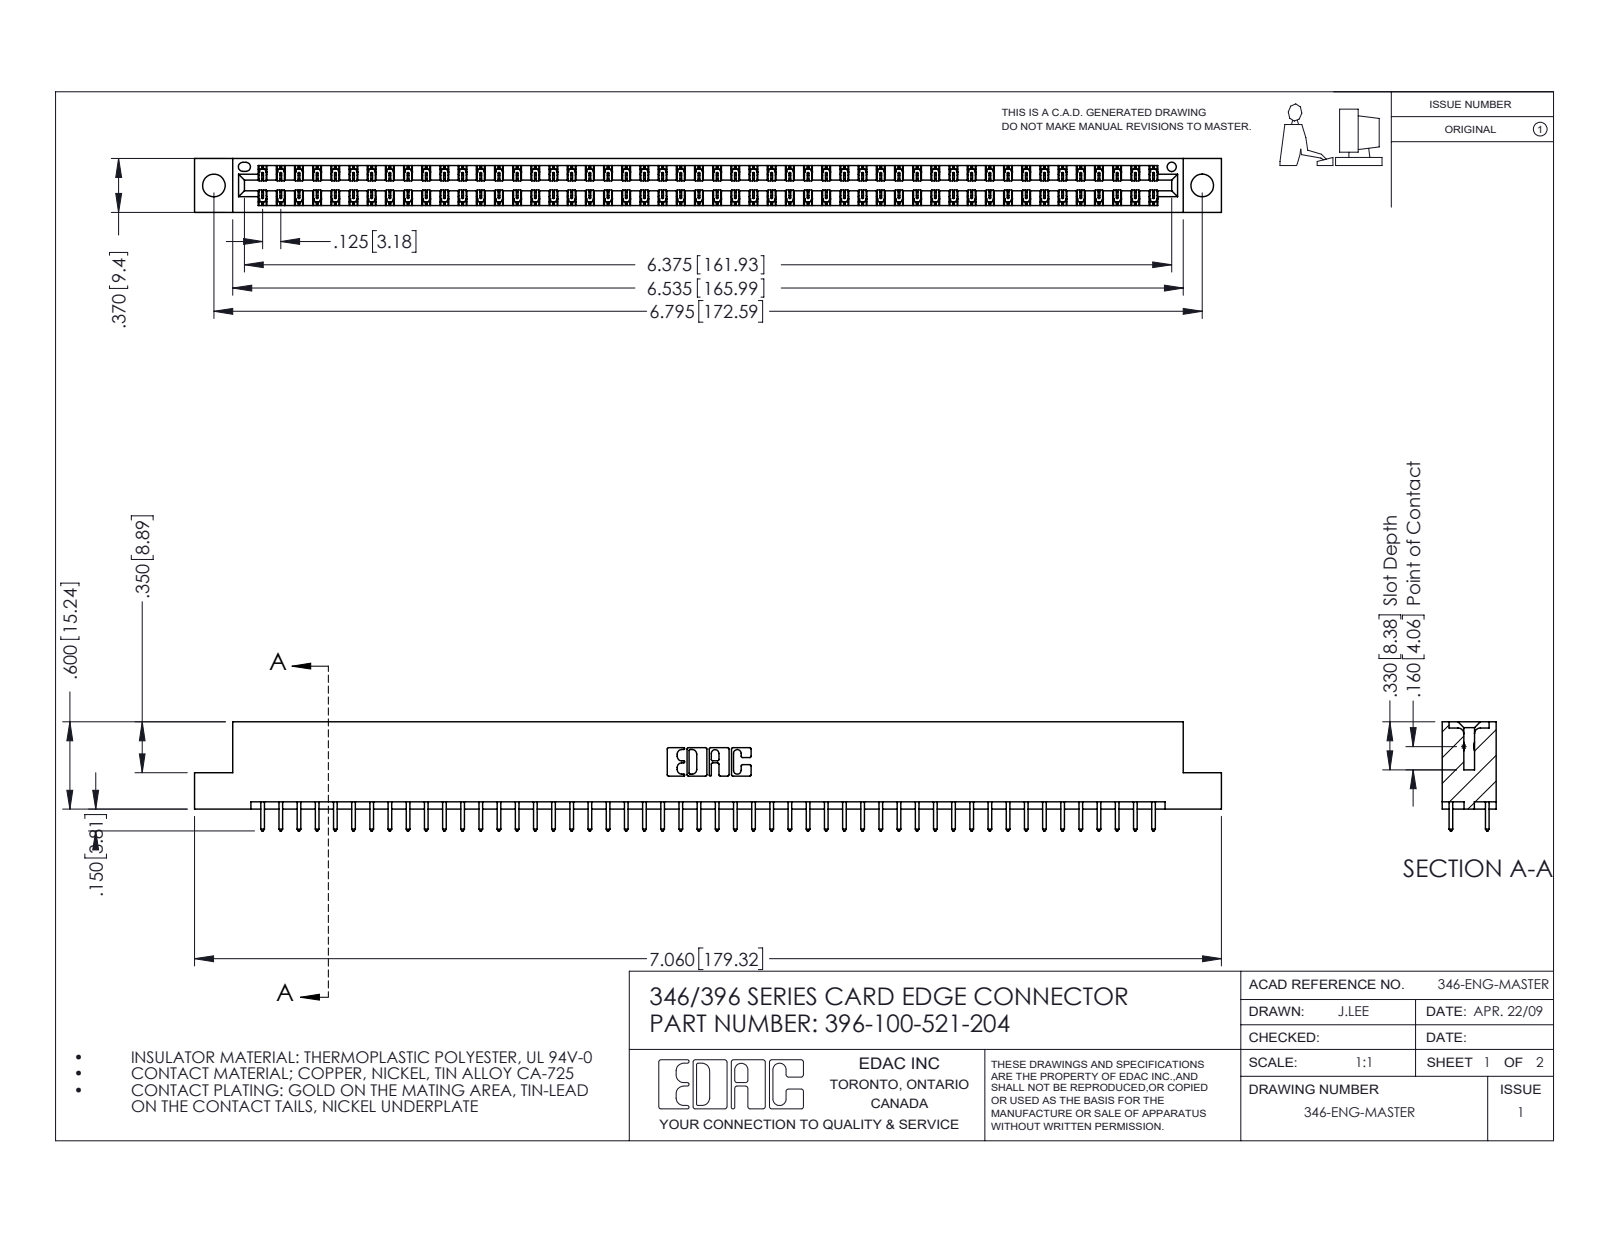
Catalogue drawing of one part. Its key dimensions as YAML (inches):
part_name: "396-100-521-204; 345-292-001_345-293-121; 346 Part_Flush Mounting Lugs - 0.156 Dia-TH"
step_written_by: "SolidWorks 2016 (CONFIG_CONTROL_DESIGN)"
units: inches
bodies: {solids: 101, faces: 5322, planar: 3576, cylindrical: 1746, other: 0}
overall_size: [7.06, 0.75, 0.37]
volume: 1.063
surface_area: 36.59
round_holes:
  - {diameter: 0.156, count: 2}
  - {diameter: 0.064, count: 1}
partial_cylinders:
  - {radius: 0.006, count: 150}
  - {radius: 0.01, count: 100}
  - {radius: 0.01, count: 22}
  - {radius: 0.007, count: 6}
  - {radius: 0.031, count: 6}
  - {radius: 0.026, count: 3}
  - {radius: 0.014, count: 2}
  - {radius: 0.022, count: 2}
face_to_face_distances: [0.048, 0.322, 0.25, 0.37, 0.072, 0.298, 0.025, 0.275, 0.148, 0.222]
hole_center_spacings: [0.246, 6.586, 6.795]
